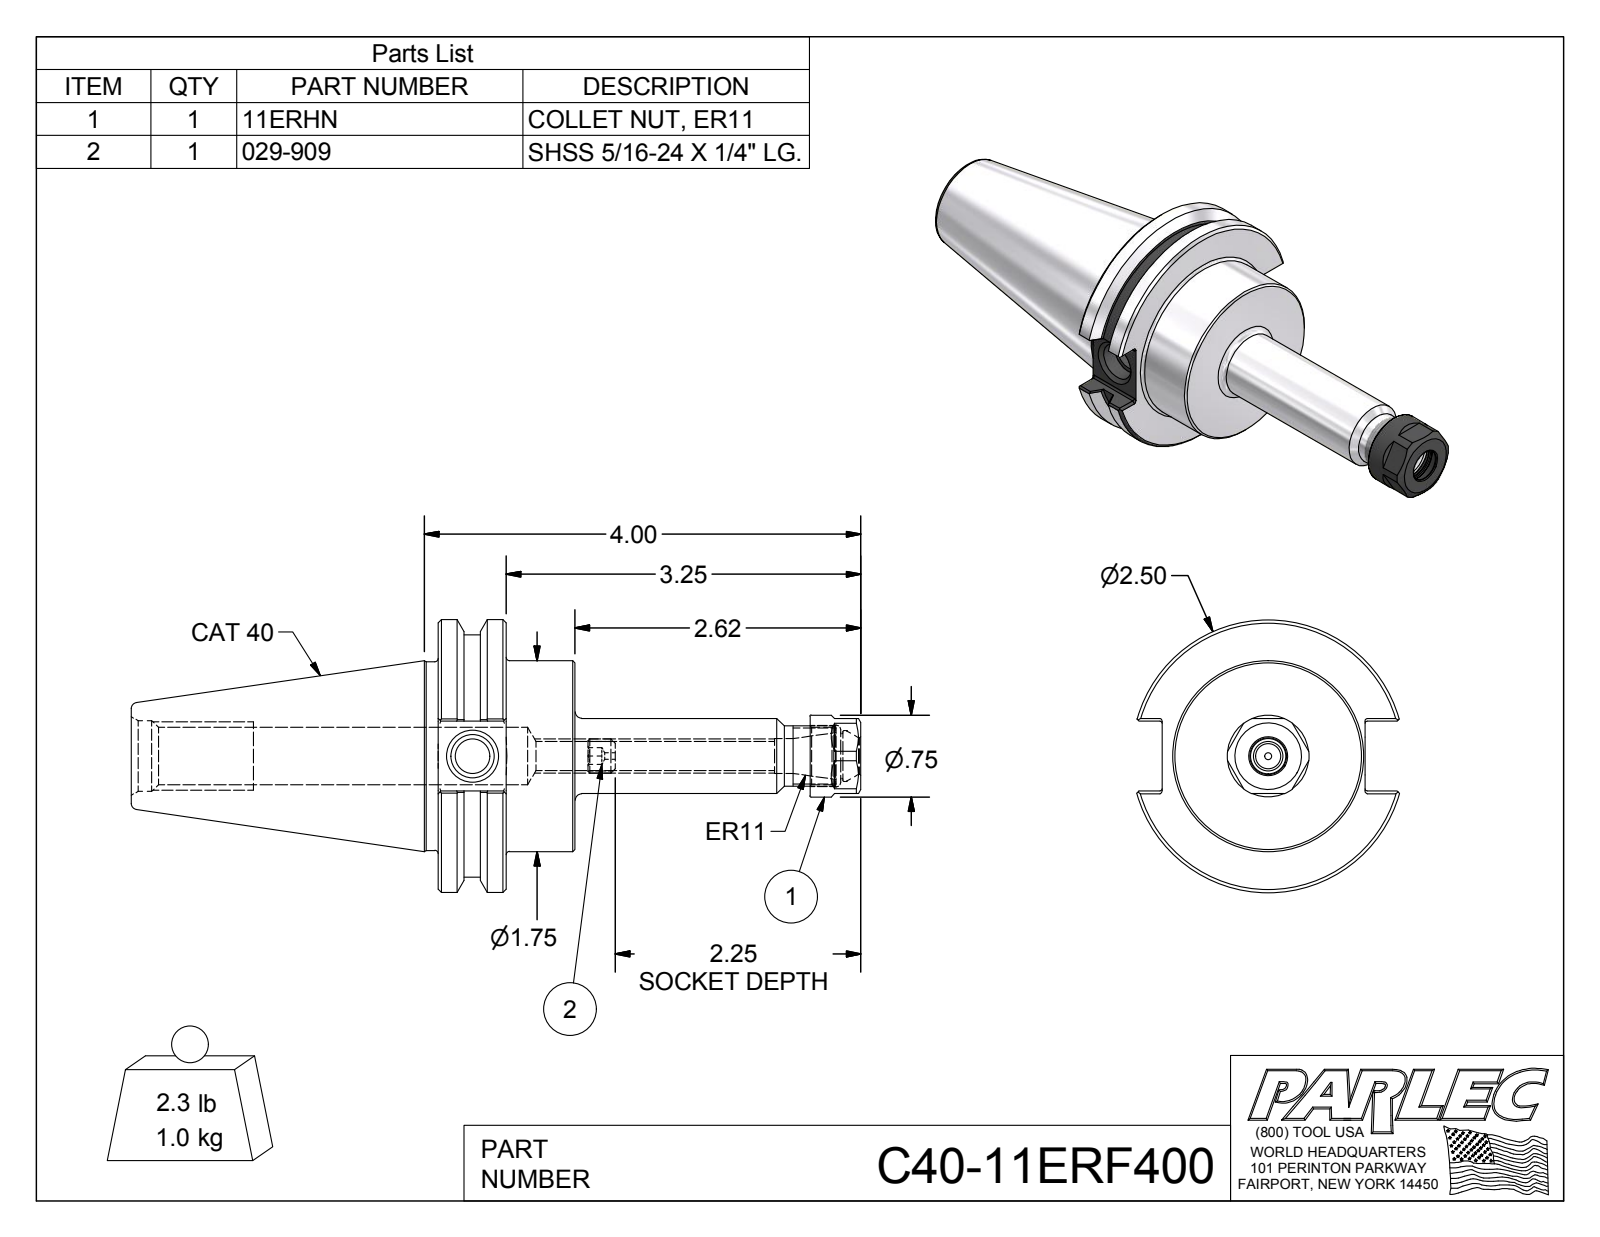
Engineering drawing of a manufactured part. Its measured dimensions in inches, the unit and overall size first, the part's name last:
Units: inches
Overall size (bounding box): 6.687 × 2.5 × 2.406
Round holes (diameter × count): ⌀0.06 ×1, ⌀0.267 ×1, ⌀0.315 ×1, ⌀0.32 ×1, ⌀0.335 ×1, ⌀0.399 ×1, ⌀0.465 ×1, ⌀0.525 ×1, ⌀0.527 ×1, ⌀0.565 ×1, ⌀0.648 ×1
Round bosses / shafts (diameter × count): ⌀2.5 ×1, ⌀2.219 ×1, ⌀1.75 ×1, ⌀1.73 ×1, ⌀0.75 ×1, ⌀0.688 ×1, ⌀0.551 ×1, ⌀0.313 ×1
Partial cylindrical surfaces — rounded edges, fillets, slot ends (radius × count): R0.02 ×12
Main face-to-face distances: 1.255, 0.625, 0.63, 0.64, 1.86, 3.875, 3.25, 2.62, 2.812, 3.437
Volume: 8.352 in³ · Surface area: 45.35 in²
Bodies: 3 solids, 148 faces (63 planar, 35 cylindrical, 50 other)
Part name (STEP PRODUCT): C40-11ERF400; C40-11ER4-1; 11ERHN; 029-909
STEP written by: Autodesk Inventor 2012 (AUTOMOTIVE_DESIGN)
